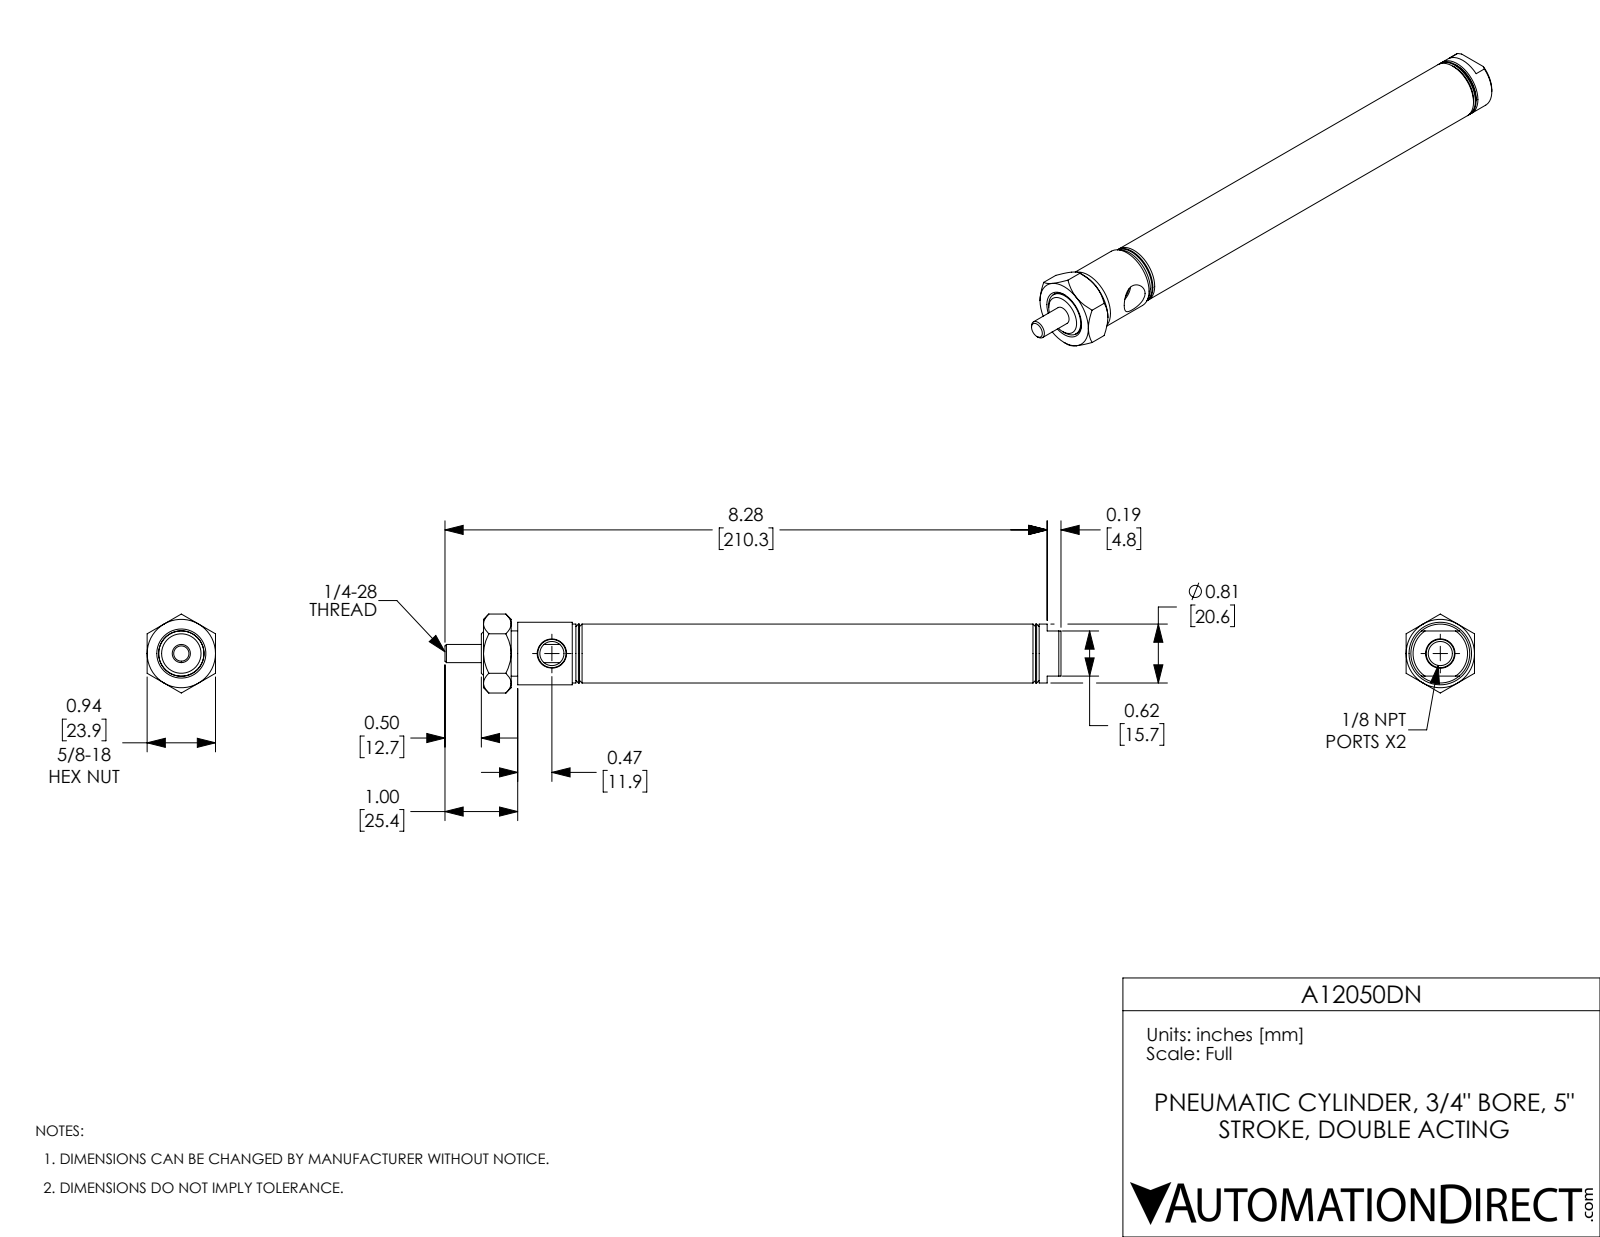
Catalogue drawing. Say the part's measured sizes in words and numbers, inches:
The part is named "A12050DN; A12050DN_Mounting Nut_D-9; A12050DN-Rod; A12050DN-MainBody". Its 3-D file was written by "SolidWorks 2017 (AUTOMOTIVE_DESIGN)". It is 3 solids with 94 faces: 27 planar, 28 cylindrical and 39 other. Overall it measures 8.47 by 1.085 by 0.94 inches. Its volume is 2.126 cubic inches and its surface area 47.95 square inches. Round holes: 2 of diameter 0.332, 1 of diameter 0.25, 1 of diameter 0.625, 1 of diameter 0.75. Round bosses or shafts: 1 of diameter 0.86, 1 of diameter 0.81, 1 of diameter 0.623. The main face-to-face distances are 6.485, 0.94, 0.5, 0.985, 1.485, 5.5, 5, 6.575, 6.075, 1.075.
